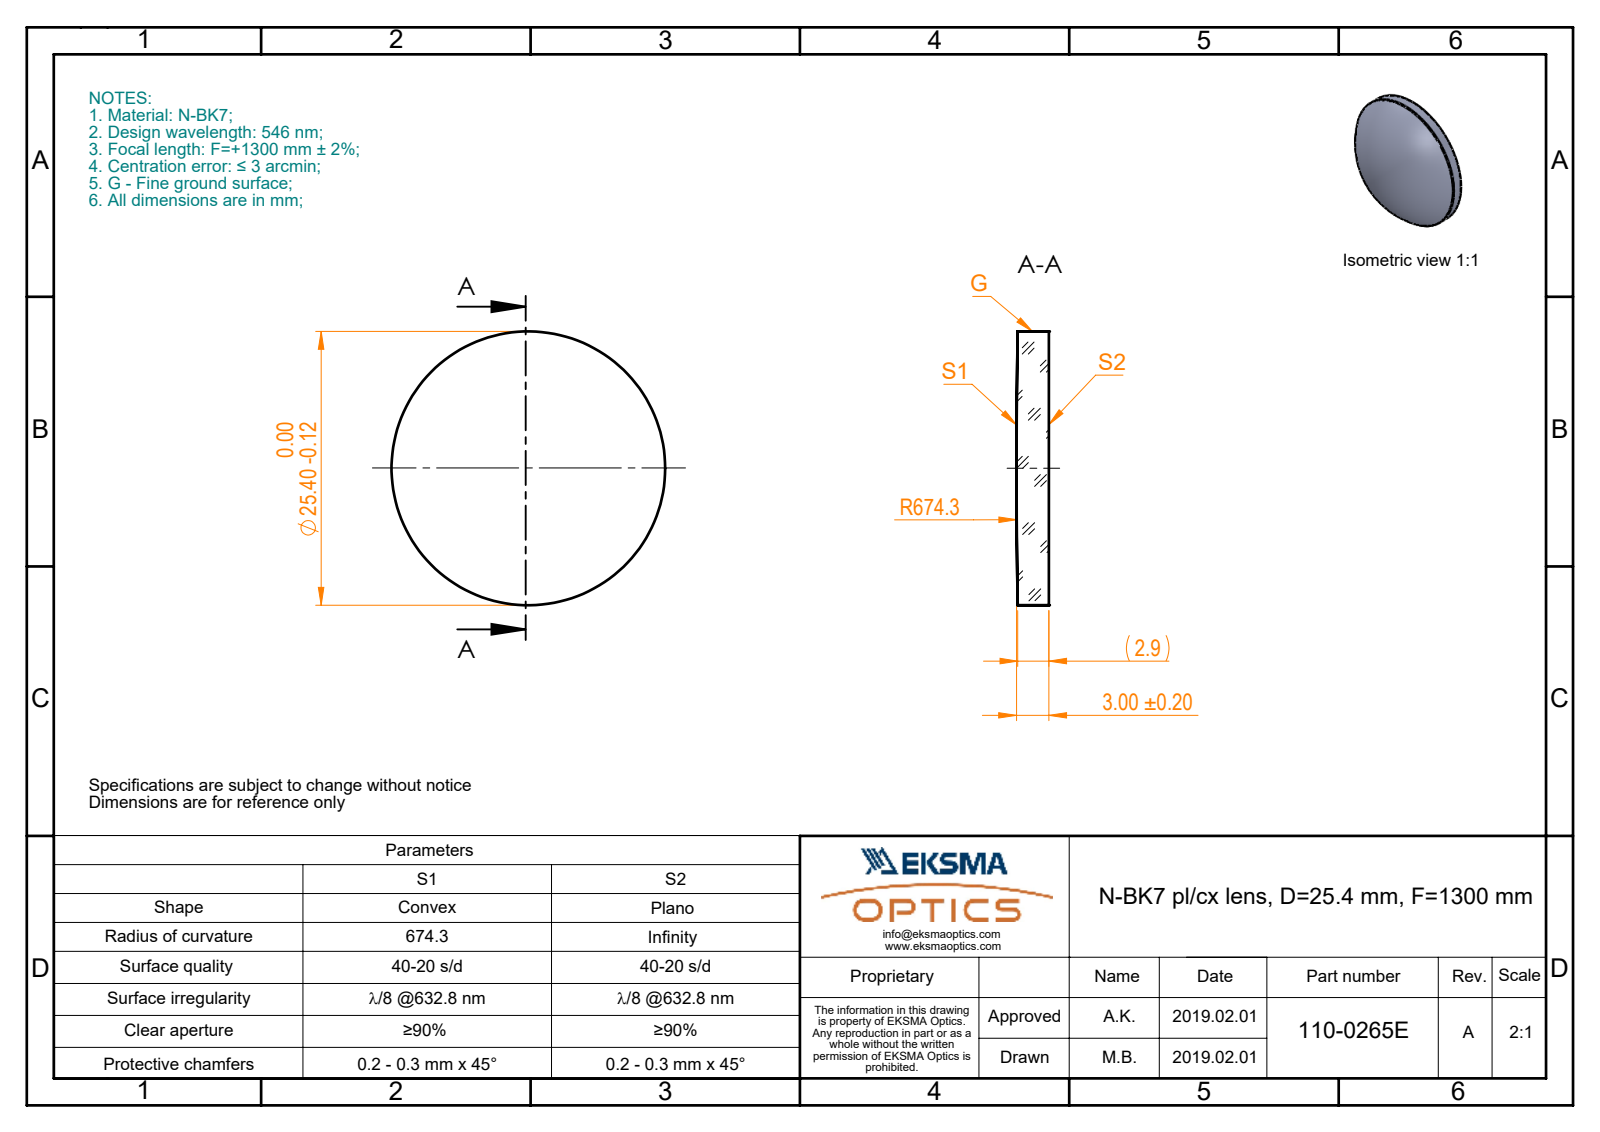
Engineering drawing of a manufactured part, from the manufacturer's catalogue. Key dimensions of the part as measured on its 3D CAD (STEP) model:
Part name (STEP PRODUCT): 110-0265E BK7 pl-cx 25.4 F1300
STEP written by: SolidWorks 2017 (CONFIG_CONTROL_DESIGN)
Units: millimetres
Bodies: 1 solid, 5 faces (1 planar, 2 cylindrical, 2 other)
Overall size (bounding box): 25.4 × 25.4 × 3
Volume: 1 490 mm³ · Surface area: 1 243 mm²
Round bosses / shafts (diameter × count): ⌀25.4 ×1
